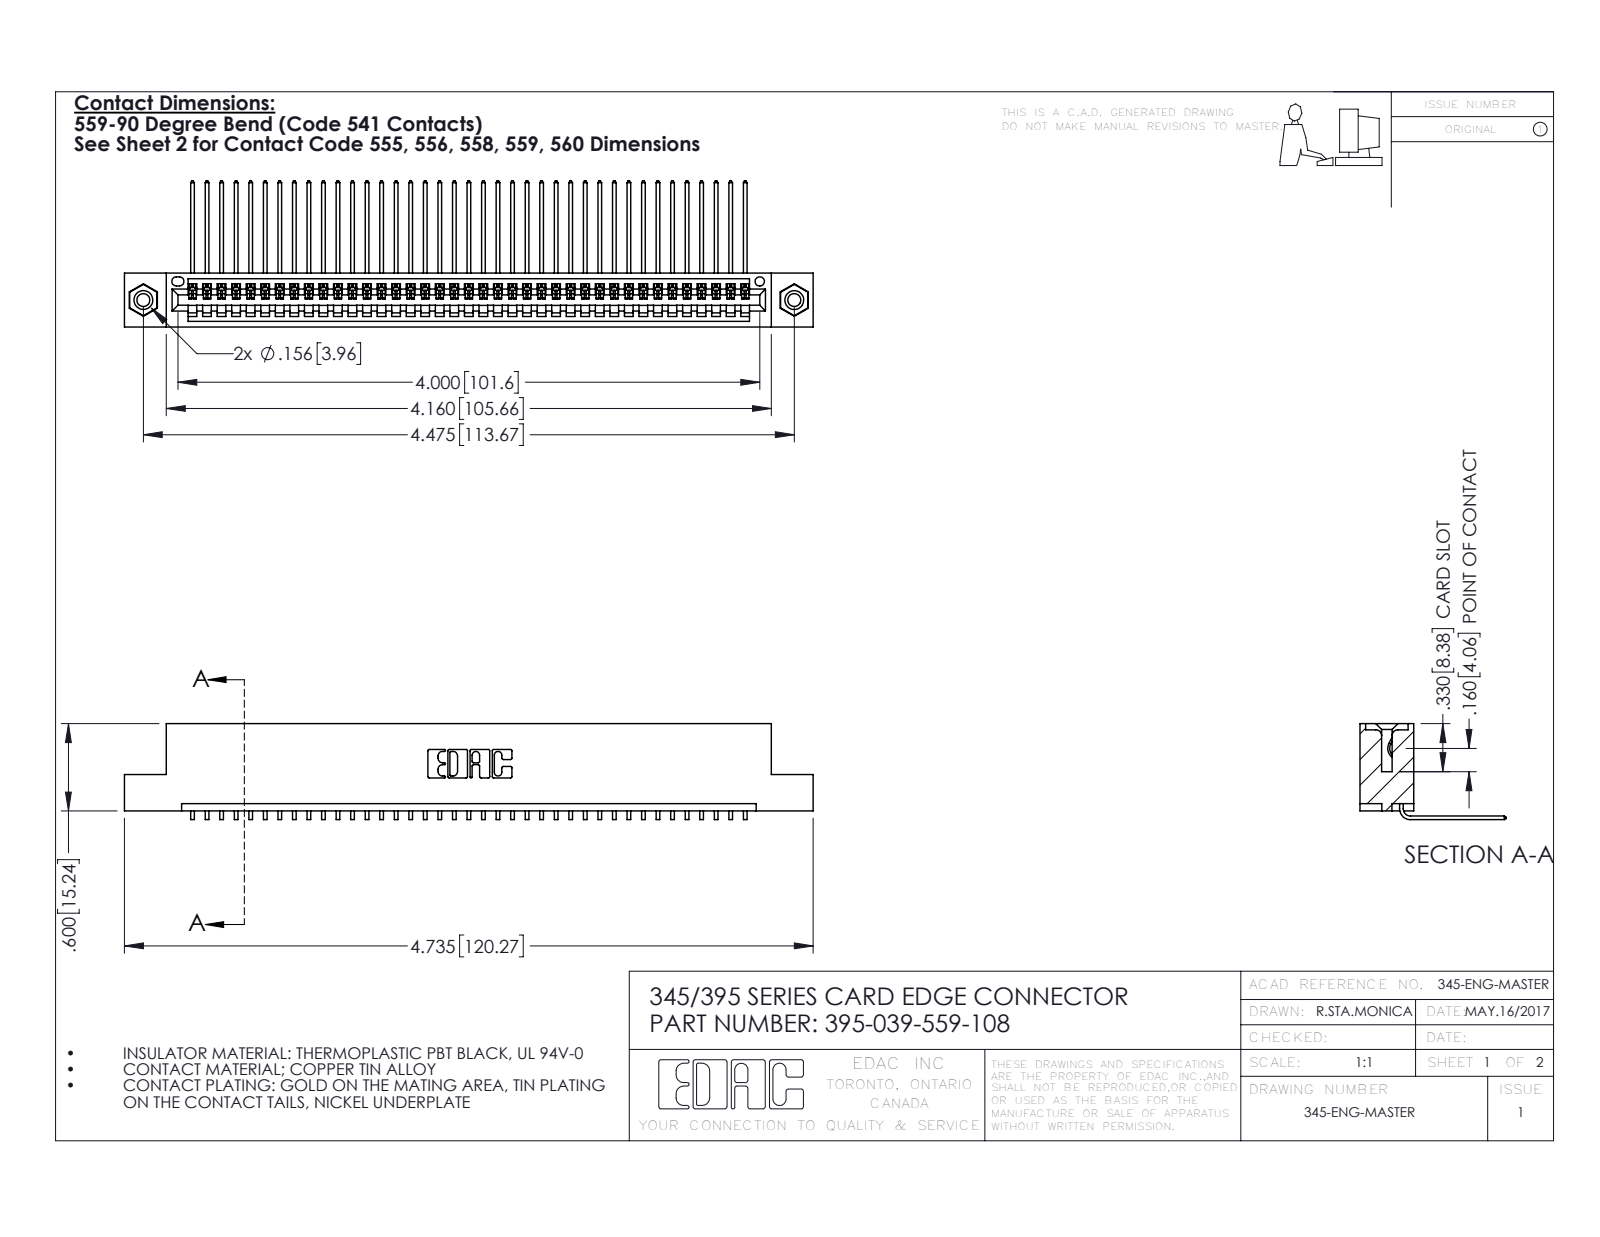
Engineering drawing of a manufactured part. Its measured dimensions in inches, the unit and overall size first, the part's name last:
Units: inches
Overall size (bounding box): 4.735 × 1.005 × 0.659
Round holes (diameter × count): ⌀0.089 ×2, ⌀0.125 ×2, ⌀0.156 ×2, ⌀0.064 ×1
Round bosses / shafts (diameter × count): ⌀0.155 ×2
Partial cylindrical surfaces — rounded edges, fillets, slot ends (radius × count): R0.006 ×78, R0.01 ×22, R0.007 ×6, R0.031 ×6, R0.026 ×3, R0.031 ×2, R0.04 ×2, R0.014 ×1
Main face-to-face distances: 0.072, 0.298, 0.37, 0.2, 0.098, 0.272, 0.025, 0.225, 0.149, 0.072
Hole centre spacings: 0.27, 4.239, 4.475
Volume: 0.703 in³ · Surface area: 24.88 in²
Bodies: 42 solids, 2526 faces (1750 planar, 760 cylindrical, 16 other)
Part name (STEP PRODUCT): 345-250-001_345-250-003-102; 345-292-001_558 559 Tail - 1; 395-039-559-108; 345 Part_Flush Mounting Lugs - 0.156 Dia-TI
STEP written by: SolidWorks 2016 (CONFIG_CONTROL_DESIGN)
